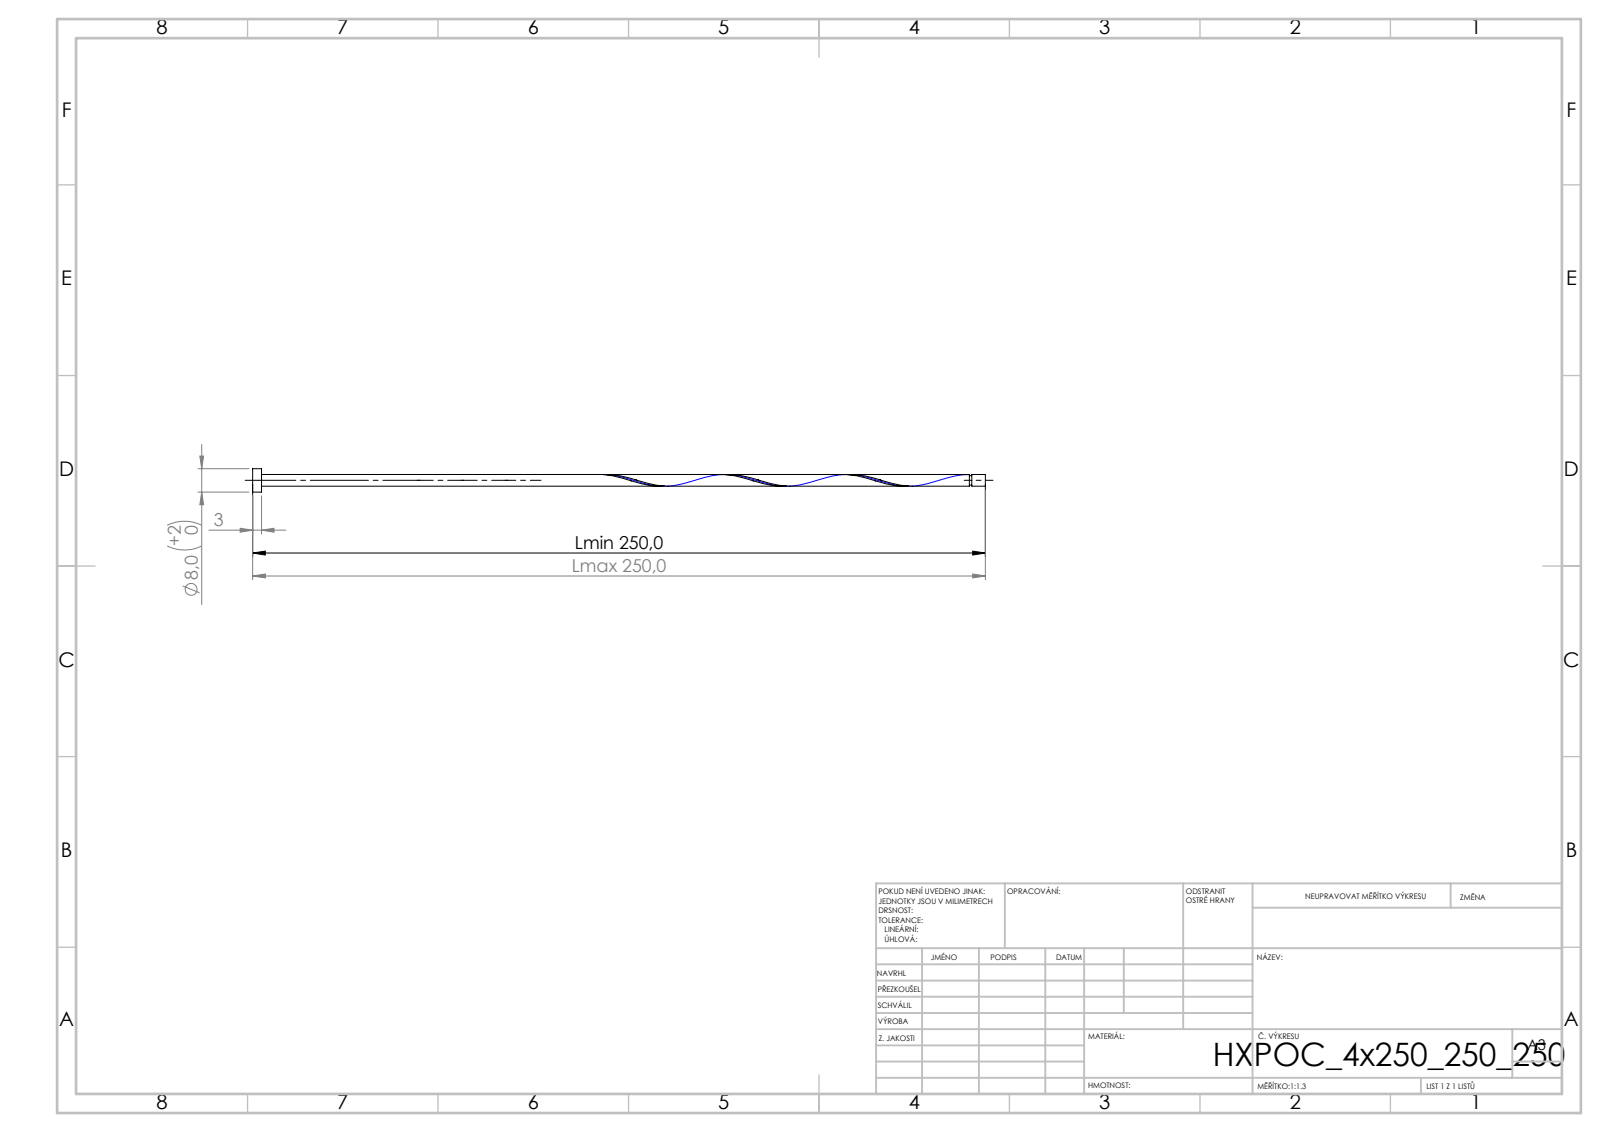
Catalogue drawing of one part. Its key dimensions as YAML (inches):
step_written_by: "SolidWorks 2019 (CONFIG_CONTROL_DESIGN)"
units: inches
bodies: {solids: 1, faces: 16, planar: 6, cylindrical: 9, other: 1}
overall_size: [9.843, 0.315, 0.315]
volume: 0.239
surface_area: 6.797
round_bosses_or_shafts:
  - {diameter: 0.315, count: 1}
  - {diameter: 0.157, count: 1}
  - {diameter: 0.126, count: 1}
face_to_face_distances: [0.118, 9.843, 9.724, 9.66, 9.542, 0.182, 9.629, 9.511, 0.031, 0.214]
